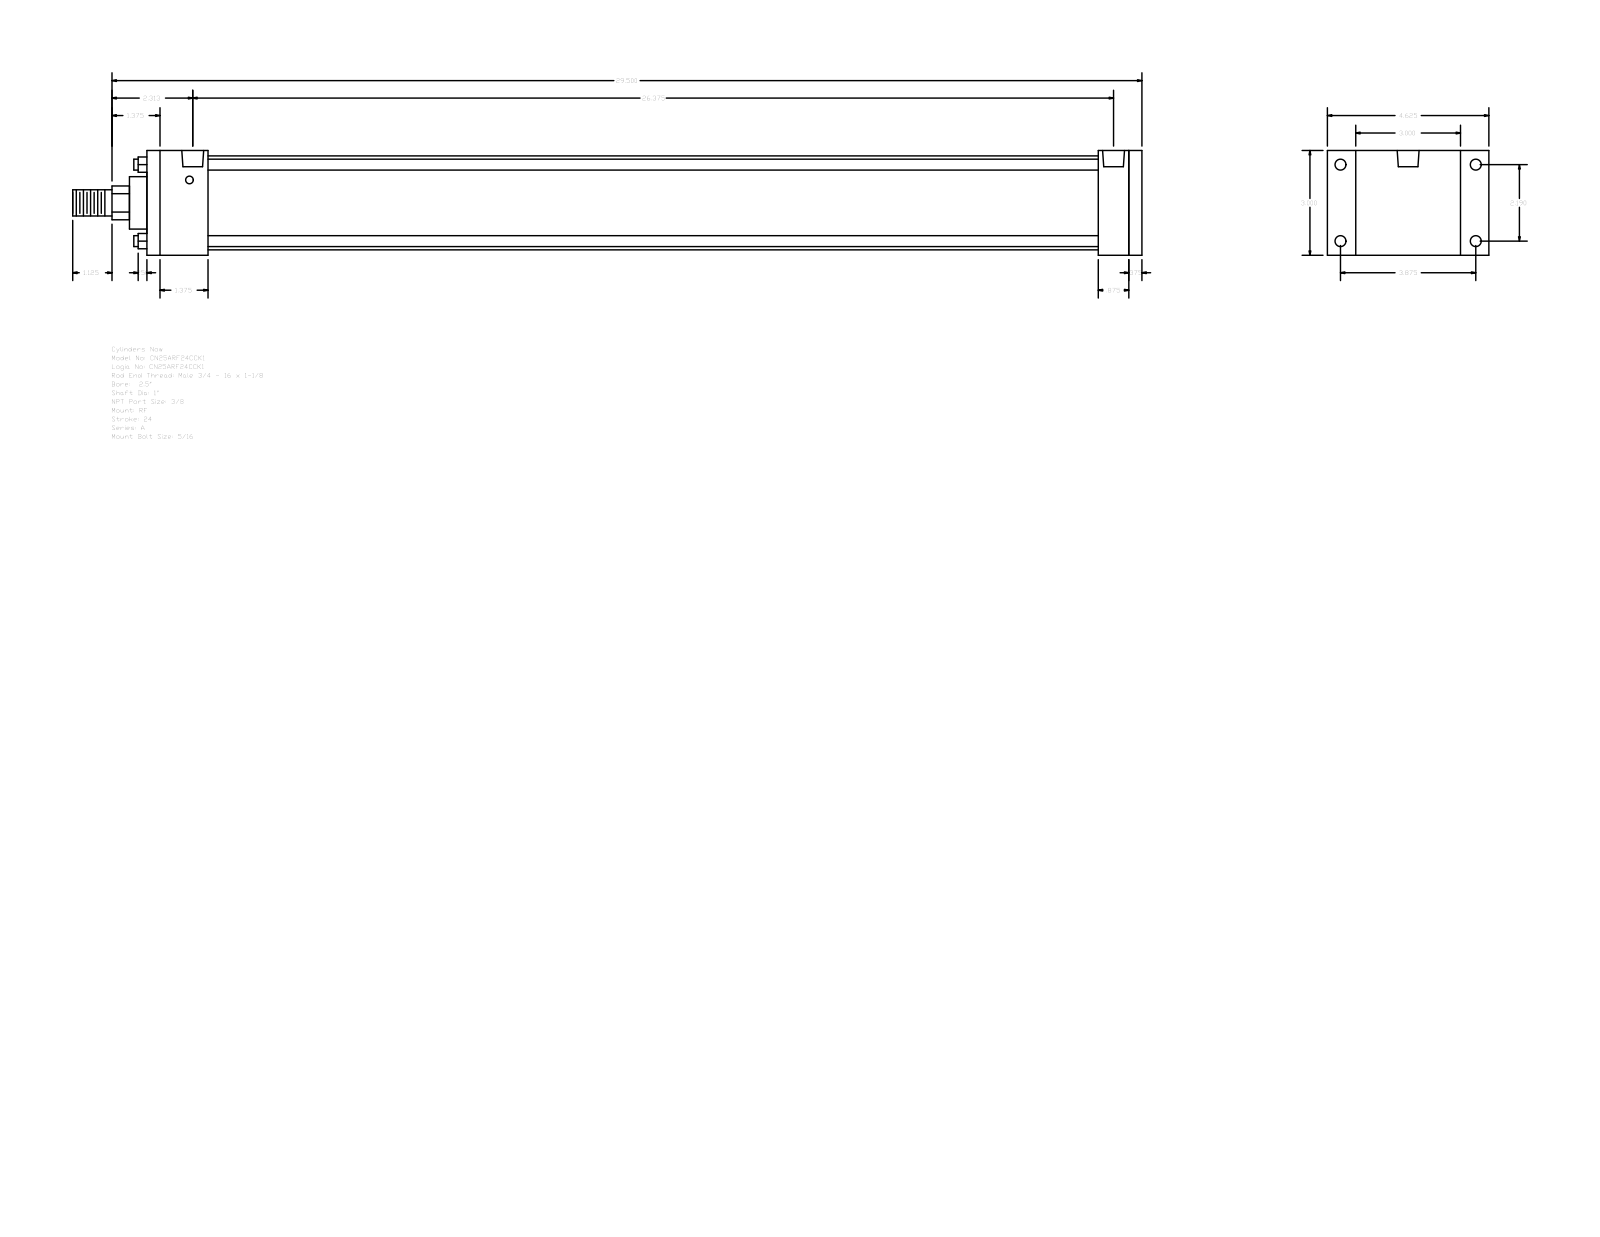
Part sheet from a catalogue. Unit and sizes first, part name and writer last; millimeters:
Units: millimetres
Overall size (bounding box): 777.88 × 117.47 × 76.2
Round holes (diameter × count): ⌀5.56 ×4, ⌀7.94 ×4, ⌀15.93 ×2
Round bosses / shafts (diameter × count): ⌀7.94 ×4, ⌀68.33 ×1, ⌀38.1 ×1, ⌀25.4 ×1, ⌀19.05 ×1
Partial cylindrical surfaces — rounded edges, fillets, slot ends (radius × count): R12.29 ×1
Main face-to-face distances: 76.2, 723.9, 9.53, 714.37, 44.45, 692.15, 647.7, 669.92, 679.45, 22.22
Hole centre spacings: 2.38, 55.62, 98.42, 113.05, 672.3, 674.68, 669.92
Bodies: 0 solids, 92 faces (64 planar, 28 cylindrical, 0 other)
Part name (STEP PRODUCT): A_RF__0250_1
STEP written by: GSSL Pune (CONFIG_CONTROL_DESIGN)
